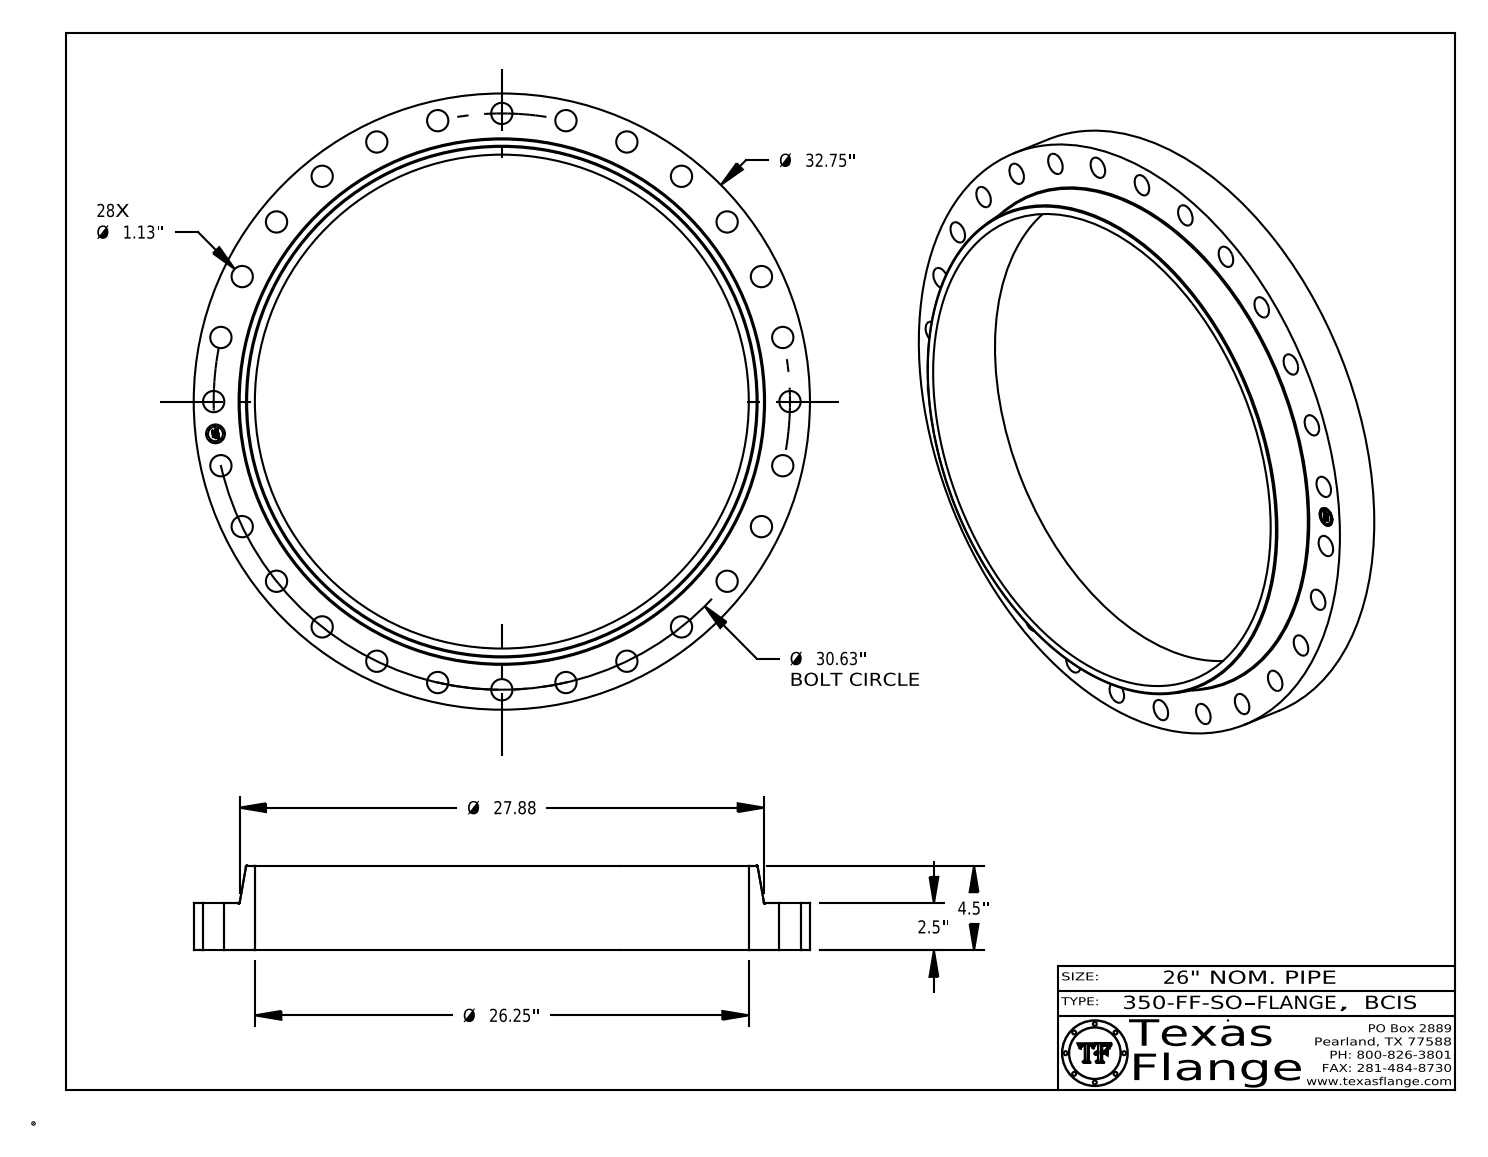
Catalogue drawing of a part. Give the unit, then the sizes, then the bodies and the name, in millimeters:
Units: millimetres
Overall size (bounding box): 831.9 × 831.9 × 114.3
Round holes (diameter × count): ⌀28.7 ×28, ⌀25.4 ×1, ⌀666.8 ×1
Round bosses / shafts (diameter × count): ⌀1.5 ×8, ⌀831.9 ×1, ⌀20 ×1
Main face-to-face distances: 63.5, 114.3, 50.8, 0.4, 63.1, 51.2, 7.6, 7.4, 1.4, 4.9
Hole centre spacings: 257, 389, 550.1, 758.5, 773.1, 87.1, 413.9, 608.3
Volume: 12 960 000 mm³ · Surface area: 1 010 000 mm²
Bodies: 1 solid, 454 faces (368 planar, 80 cylindrical, 6 other)
Part name (STEP PRODUCT): BCIS, Class 350-FF-SO
STEP written by: CATIA V5 STEP AP214 (AUTOMOTIVE_DESIGN)
